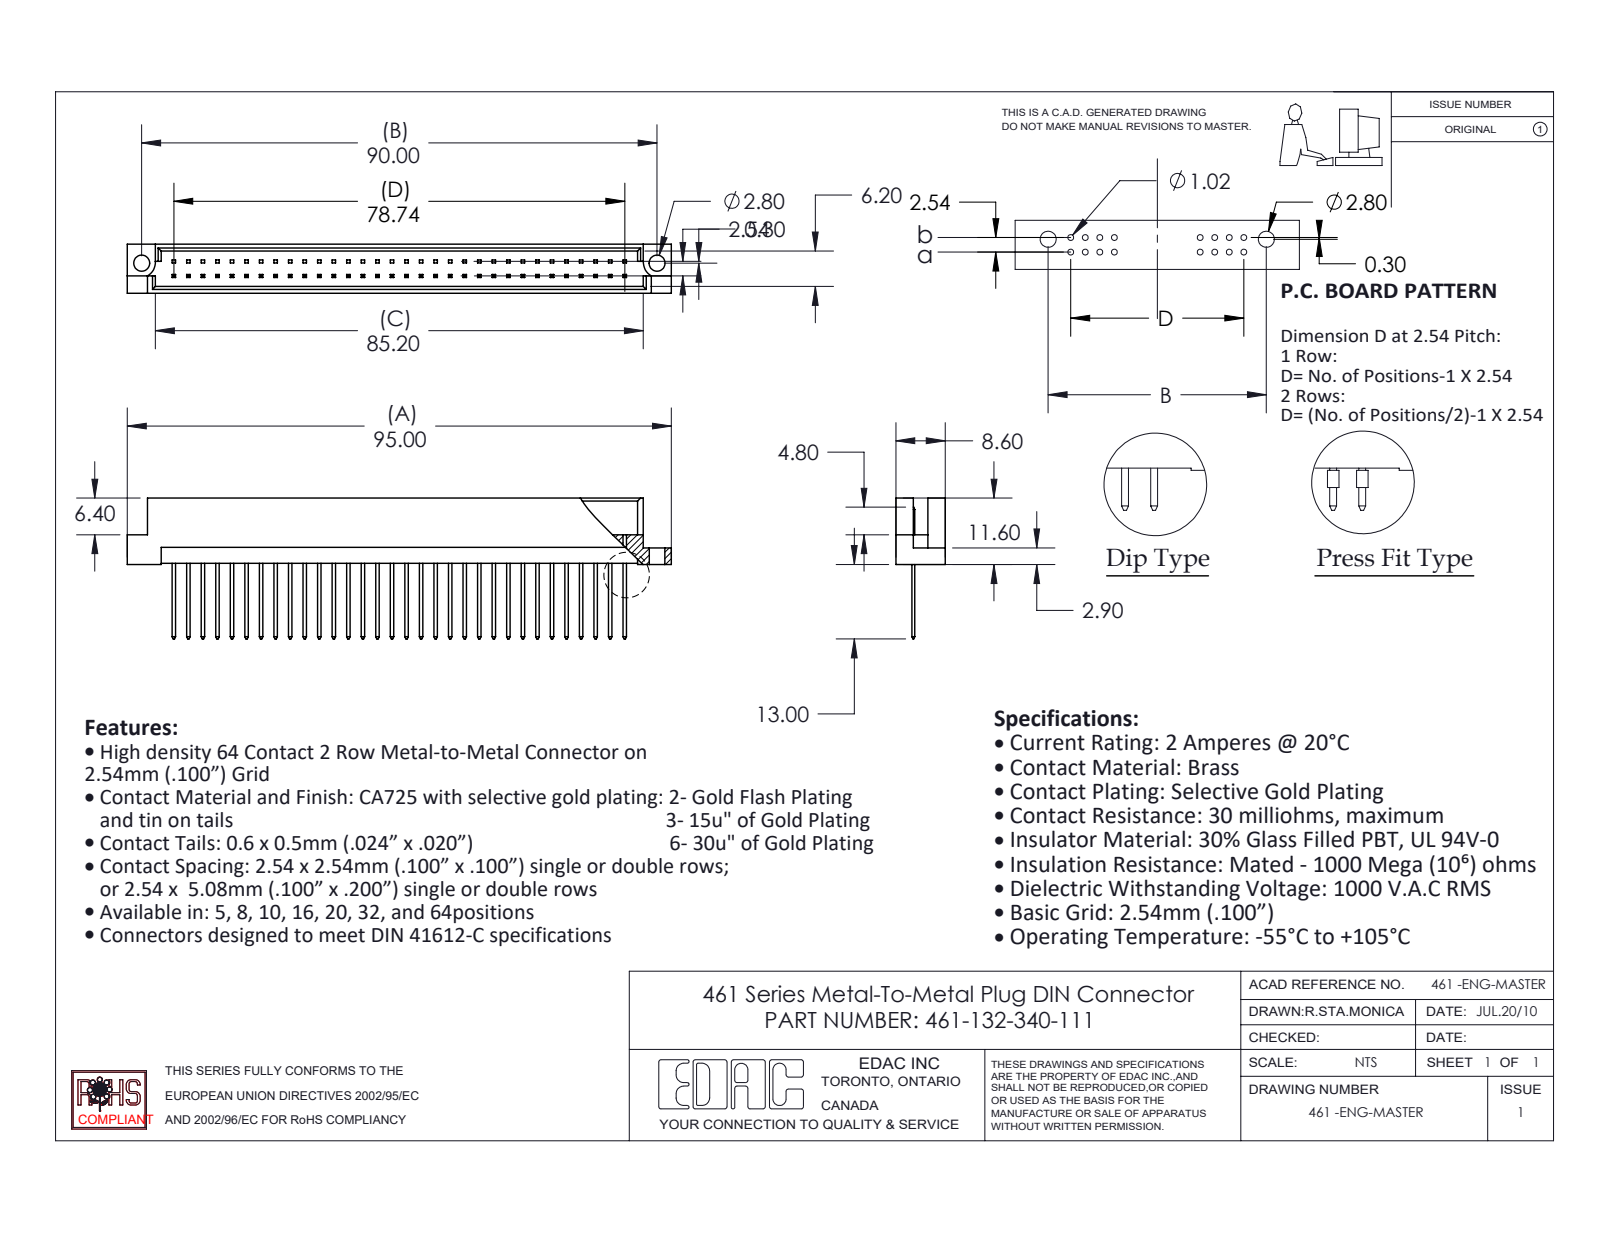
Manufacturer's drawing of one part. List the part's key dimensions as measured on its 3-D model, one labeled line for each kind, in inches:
Part name (STEP PRODUCT): 461 Part_64; 461-132-340-111; 461-290_40
STEP written by: SolidWorks 2020 (CONFIG_CONTROL_DESIGN)
Units: inches
Bodies: 33 solids, 753 faces (746 planar, 7 cylindrical, 0 other)
Overall size (bounding box): 3.74 × 0.969 × 0.339
Volume: 0.297 in³ · Surface area: 11.28 in²
Round holes (diameter × count): ⌀0.11 ×2
Partial cylindrical surfaces — rounded edges, fillets, slot ends (radius × count): R0.11 ×2
Main face-to-face distances: 0.047, 0.291, 0.339, 0.244, 0.129, 0.209, 0.082, 0.162, 0.109, 0.229
Hole centre spacings: 3.543
